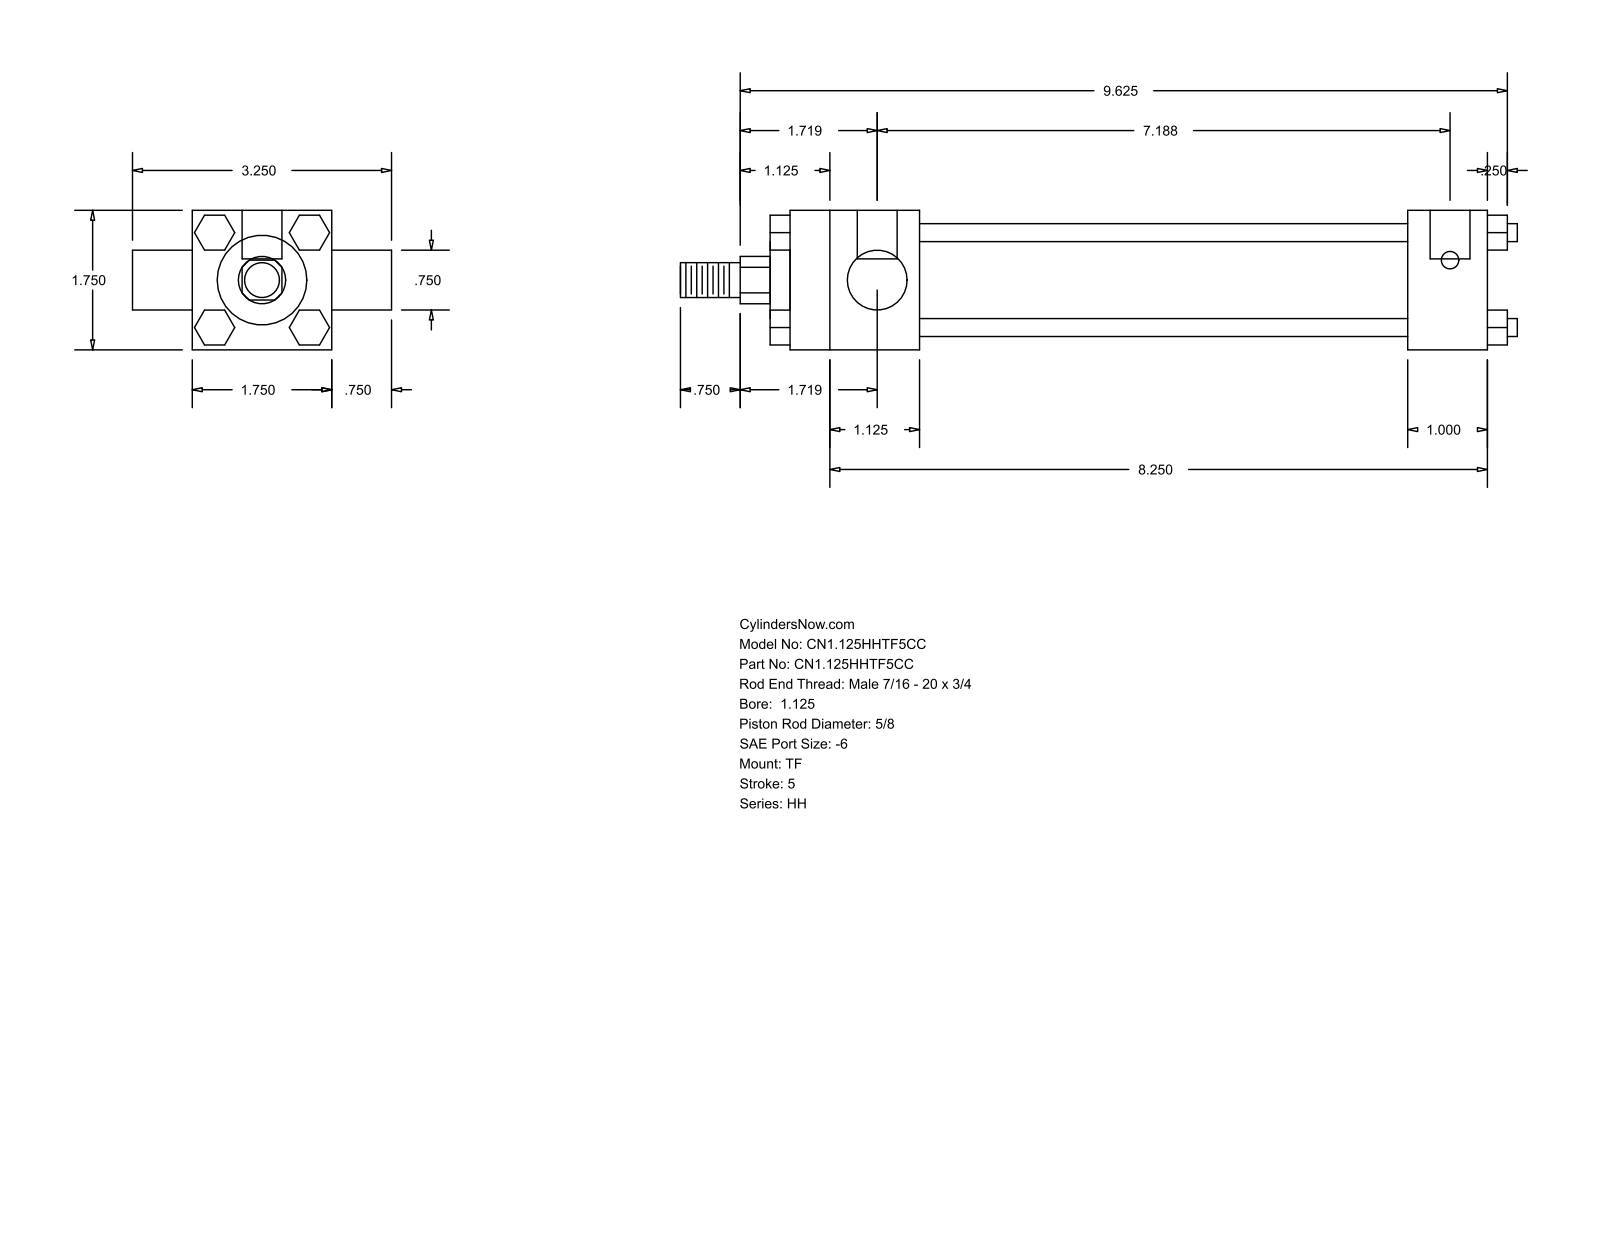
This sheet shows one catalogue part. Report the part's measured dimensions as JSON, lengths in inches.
{"part_name": "HH_TF__0112_0.625", "step_written_by": "GSSL Pune (CONFIG_CONTROL_DESIGN)", "units": "inches", "bodies": {"solids": 0, "faces": 120, "planar": 92, "cylindrical": 28, "other": 0}, "overall_size": [10.5, 3.25, 1.75], "round_holes": [[0.219, 3], [0.5, 2]], "round_bosses_or_shafts": [[0.225, 4], [1.375, 1], [1.125, 1], [0.75, 1], [0.625, 1], [0.437, 1]], "partial_cylinders_radius": [[0.297, 1]], "face_to_face_distances": [1.75, 0.25, 9, 0.437, 1, 6.125, 7.125, 1.625, 7.75, 8.75], "hole_center_spacings": [0.125, 7.063, 7.187]}
